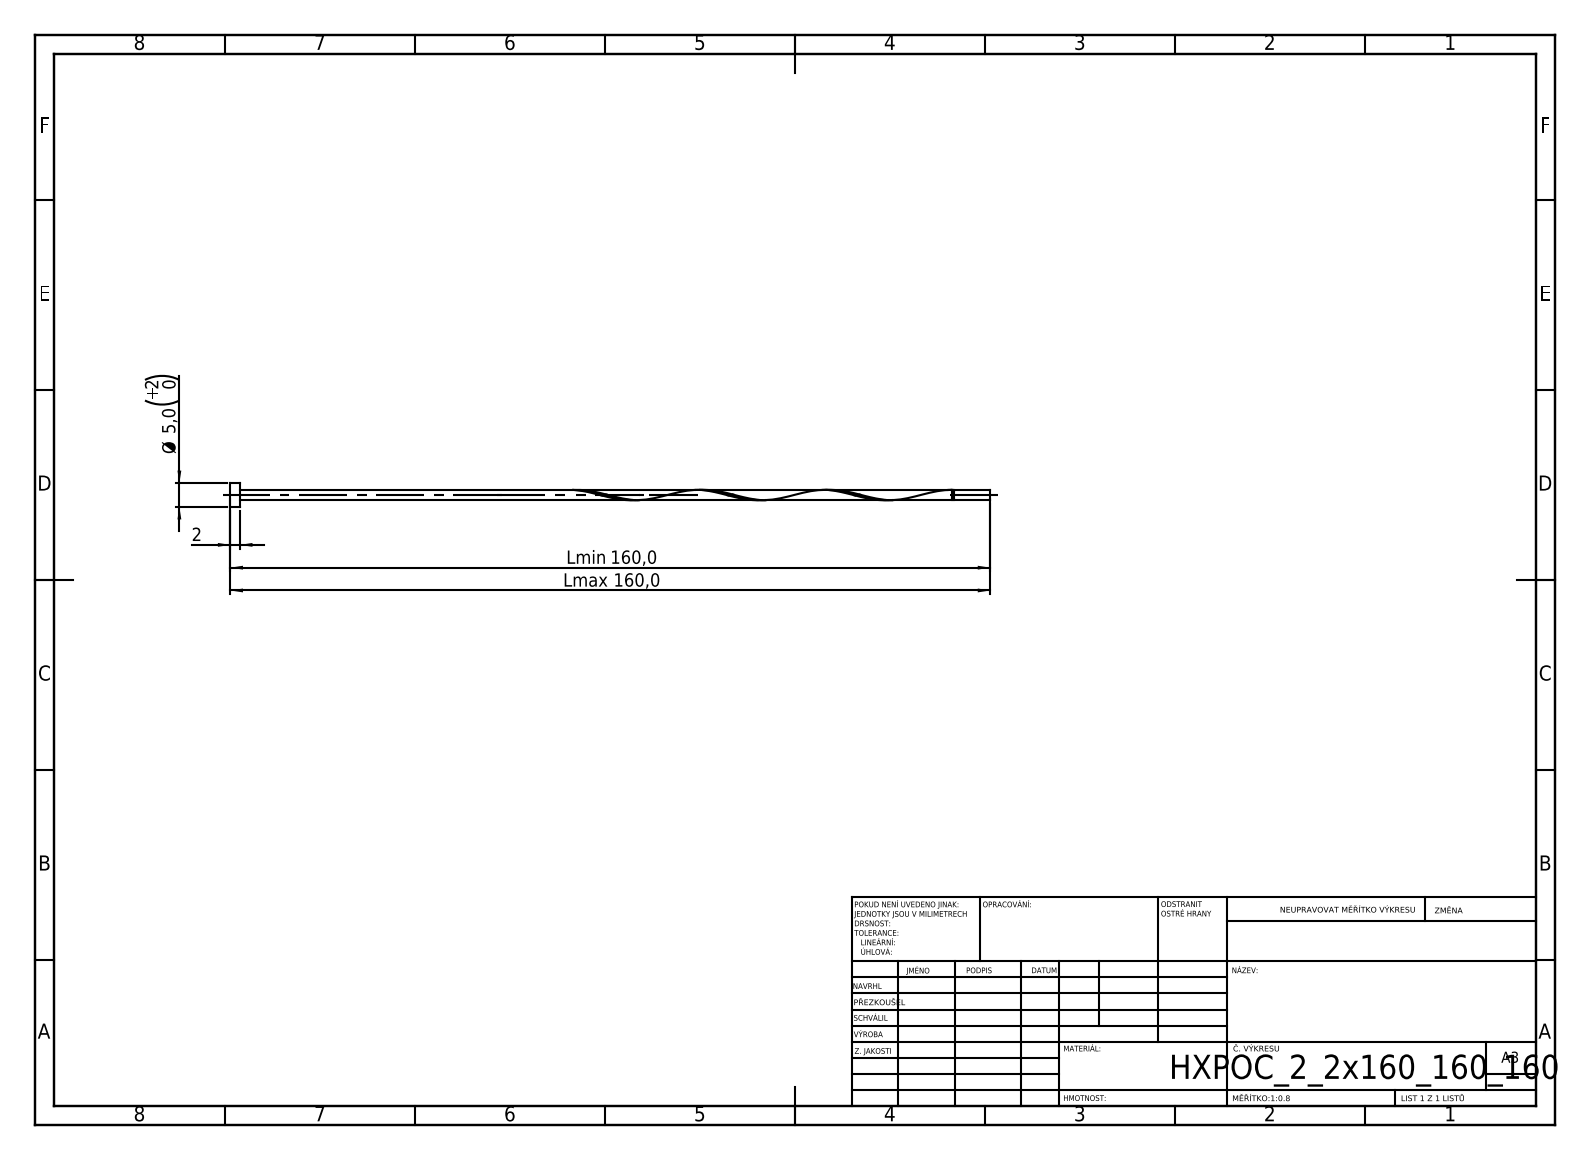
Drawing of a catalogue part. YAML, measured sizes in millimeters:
step_written_by: "SolidWorks 2019 (CONFIG_CONTROL_DESIGN)"
units: millimeters
bodies: {solids: 1, faces: 16, planar: 6, cylindrical: 9, other: 1}
overall_size: [160, 5, 5]
volume: 769
surface_area: 1551
round_bosses_or_shafts:
  - {diameter: 5, count: 1}
  - {diameter: 2.2, count: 1}
  - {diameter: 1.76, count: 1}
face_to_face_distances: [2, 160, 158, 152.45, 150.45, 7.55, 152.01, 150.01, 0.44, 7.99]
